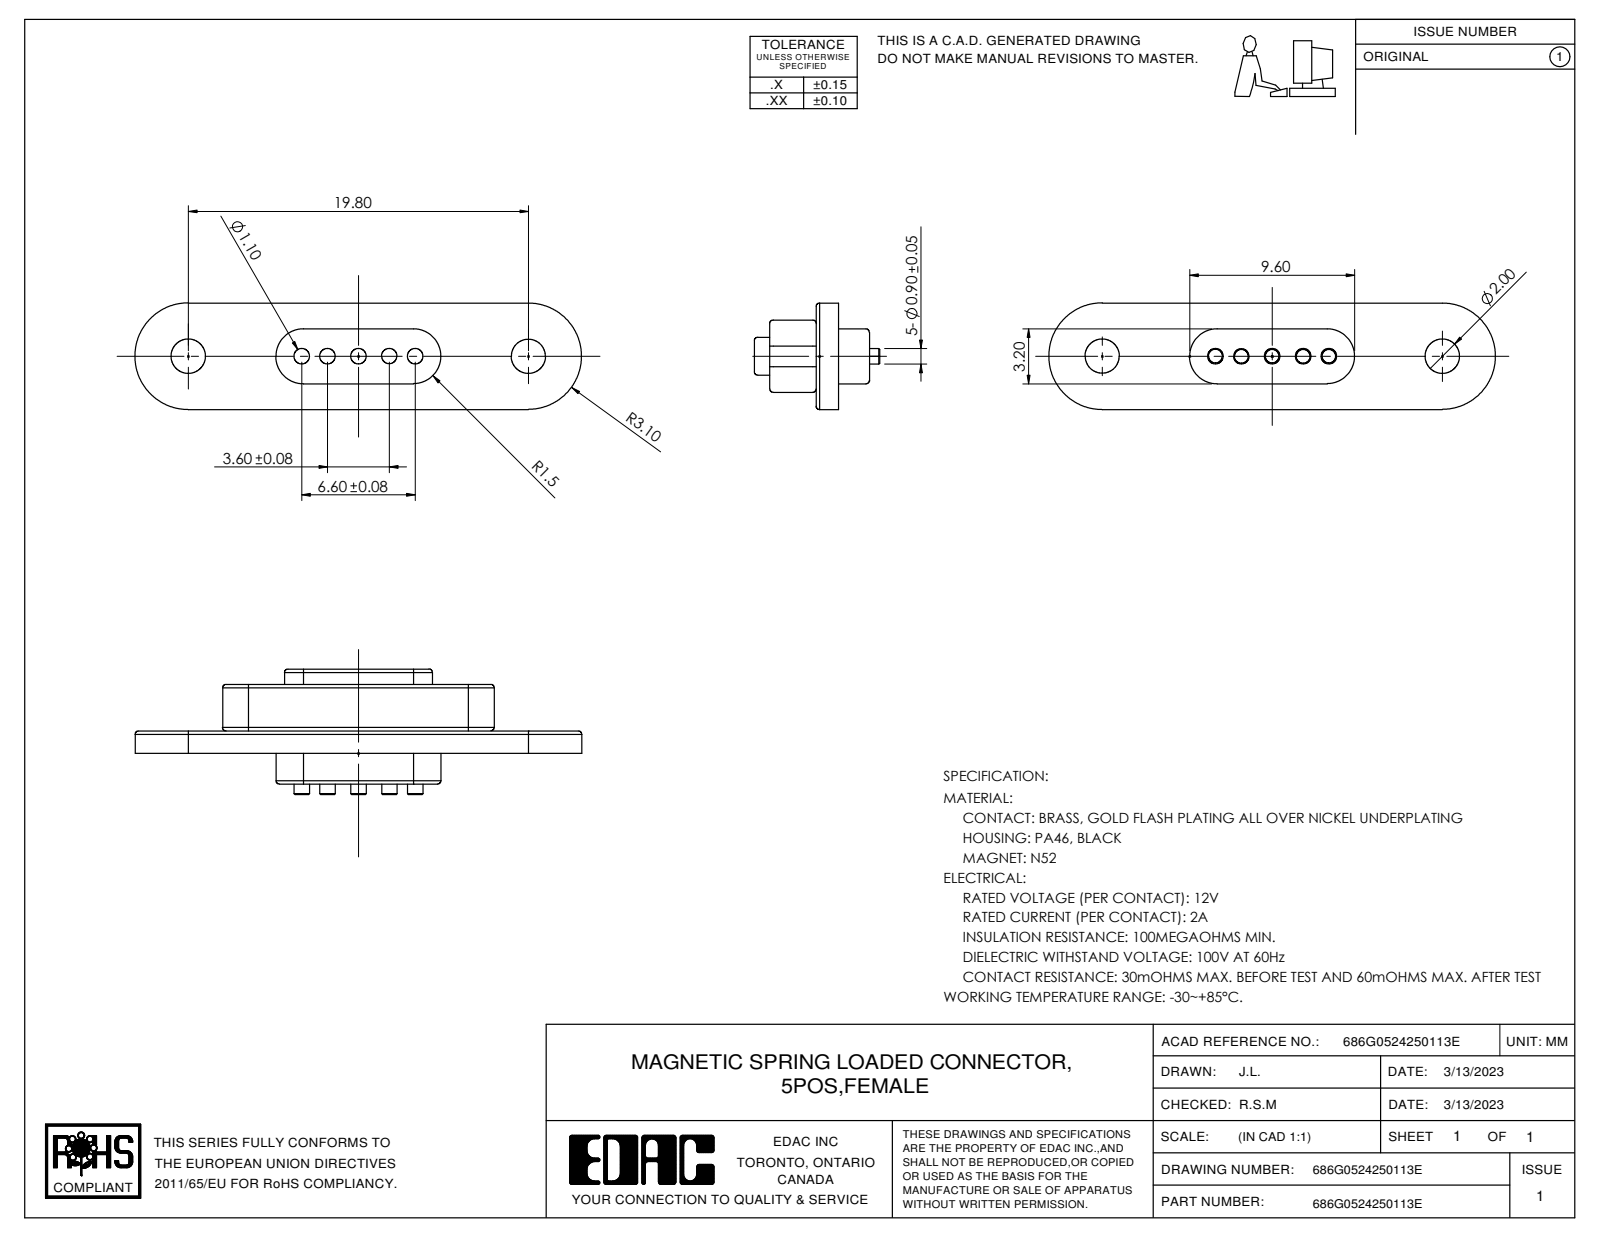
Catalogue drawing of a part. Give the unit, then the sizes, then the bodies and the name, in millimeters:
Units: millimetres
Overall size (bounding box): 26 × 7.3 × 6.2
Round holes (diameter × count): ⌀1.1 ×5, ⌀2 ×2
Round bosses / shafts (diameter × count): ⌀0.9 ×5
Partial cylindrical surfaces — rounded edges, fillets, slot ends (radius × count): R0.2 ×14, R0.1 ×6, R1.5 ×4, R0.95 ×2, R1 ×2, R1.1 ×2, R1.6 ×2, R3.1 ×2
Main face-to-face distances: 1.3, 3.1, 1, 2.7, 5.2, 2.1, 4, 4.2, 0.5, 2.15
Hole centre spacings: 6.6, 1.5, 1.8, 3.3, 5.1, 8.1, 9.9, 11.7
Volume: 427 mm³ · Surface area: 672 mm²
Bodies: 1 solid, 134 faces (31 planar, 66 cylindrical, 37 other)
Part name (STEP PRODUCT): 686-G0524250113
STEP written by: SolidWorks 2020 (CONFIG_CONTROL_DESIGN)
